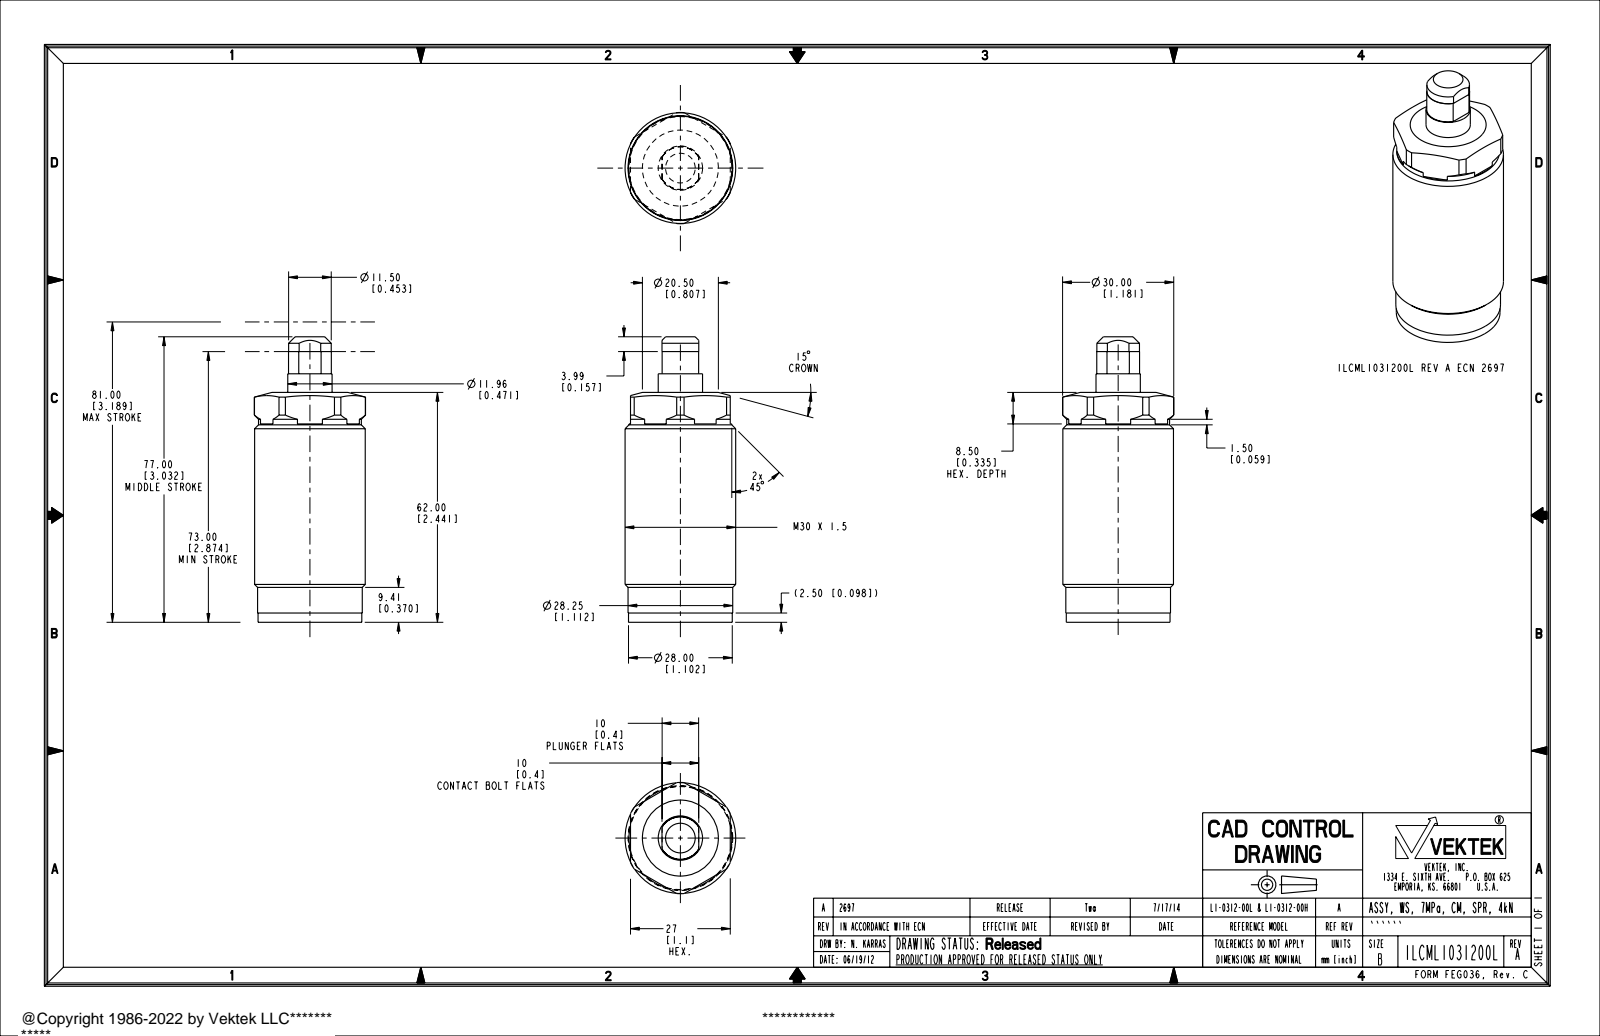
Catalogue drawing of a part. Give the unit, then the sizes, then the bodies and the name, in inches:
Units: inches
Overall size (bounding box): 3.031 × 1.181 × 1.175
Round bosses / shafts (diameter × count): ⌀1.175 ×1, ⌀1.112 ×1, ⌀1.102 ×1, ⌀1.093 ×1, ⌀0.471 ×1
Partial cylindrical surfaces — rounded edges, fillets, slot ends (radius × count): R0.226 ×1, R0.228 ×1, R0.591 ×1
Main face-to-face distances: 1.06, 2.441, 0.336, 0.724, 3.031, 0.591, 0.335, 0.387, 0.725, 0.389
Volume: 2.637 in³ · Surface area: 11.62 in²
Bodies: 1 solid, 59 faces (25 planar, 20 cylindrical, 14 other)
Part name (STEP PRODUCT): ILCML1031200L
STEP written by: PRO/ENGINEER BY PARAMETRIC TECHNOLOGY CORPORATION, 2013320 (AUTOMOTIVE_DESIGN)
